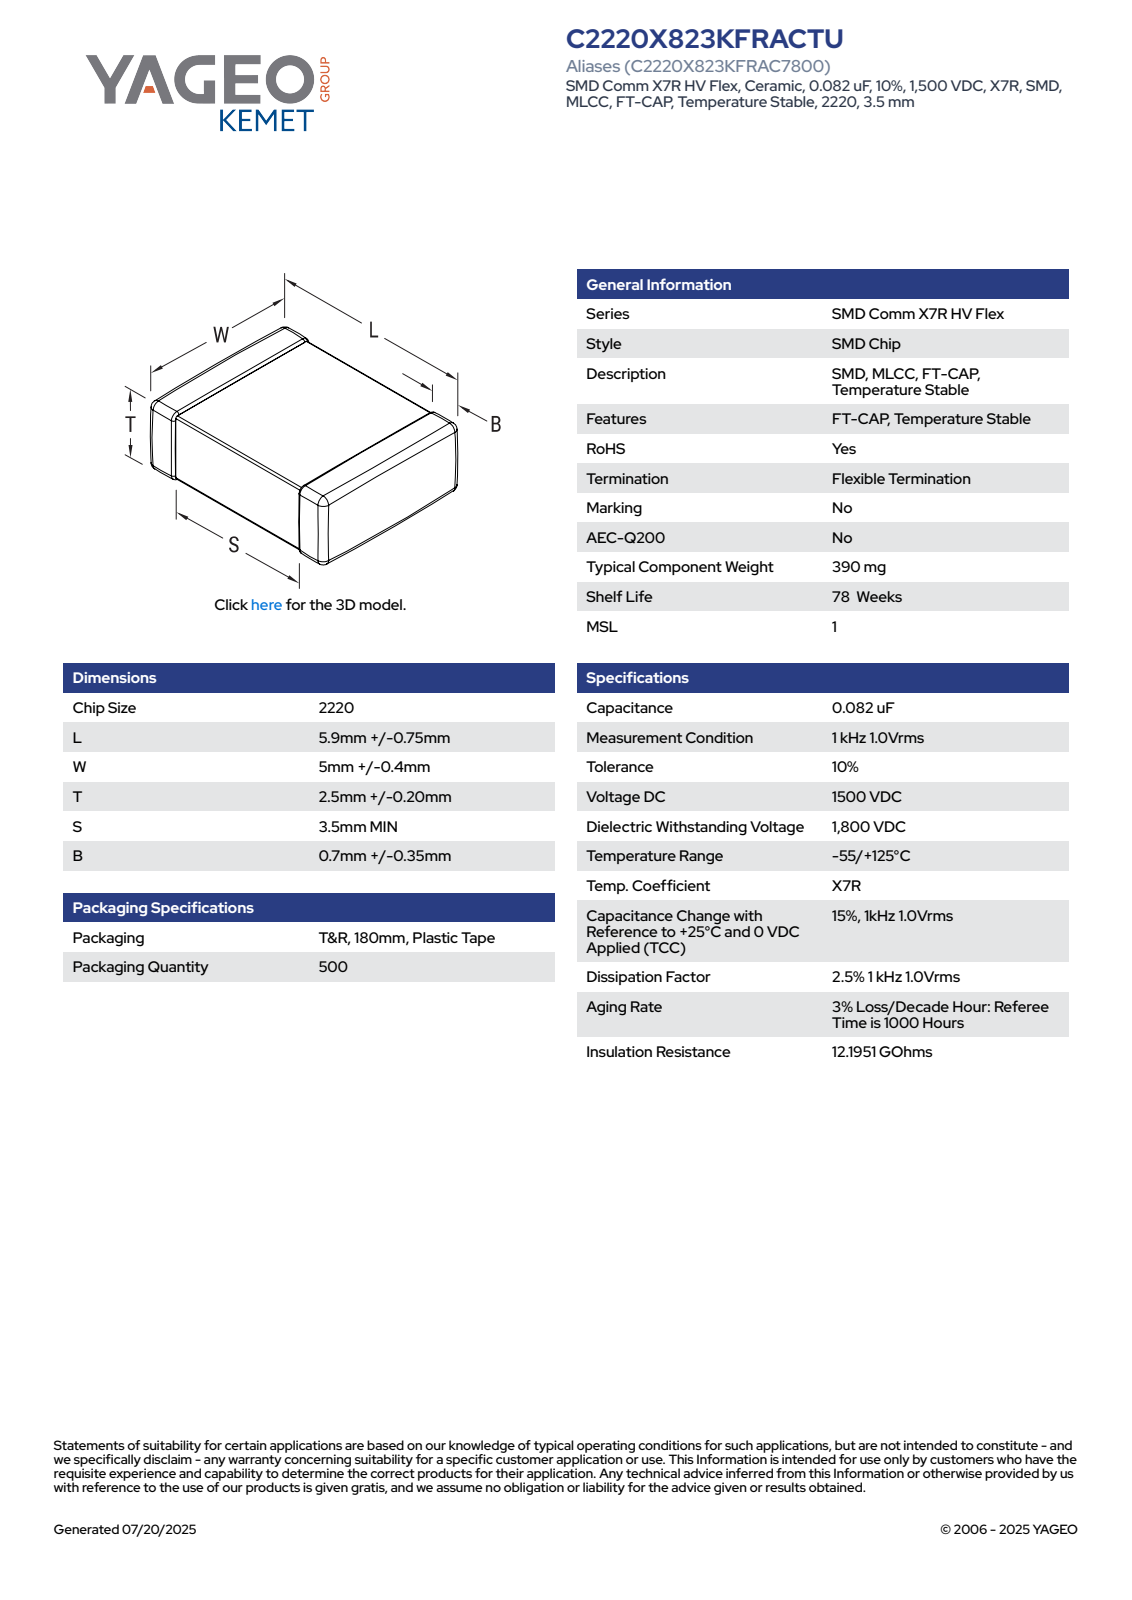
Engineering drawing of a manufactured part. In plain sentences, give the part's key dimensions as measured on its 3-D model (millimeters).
The part is named "CCS_CCSTDNOS_2220_L6.65W5.4T2.7B1.05". Its 3-D file was written by "SolidWorks 2014 (AUTOMOTIVE_DESIGN)". It is 4 solids with 125 faces: 71 planar, 38 cylindrical and 16 other. Overall it measures 6.65 by 5.4 by 2.7 millimeters. Its volume is 89 cubic millimeters and its surface area 133 square millimeters. Partial cylindrical surfaces (rounded edges, fillets, slot ends): 24 of radius 0.11. The main face-to-face distances are 2.48, 2.59, 6.65, 5.18, 2.7, 5.29, 5.4, 2.51, 2.78, 2.62.
